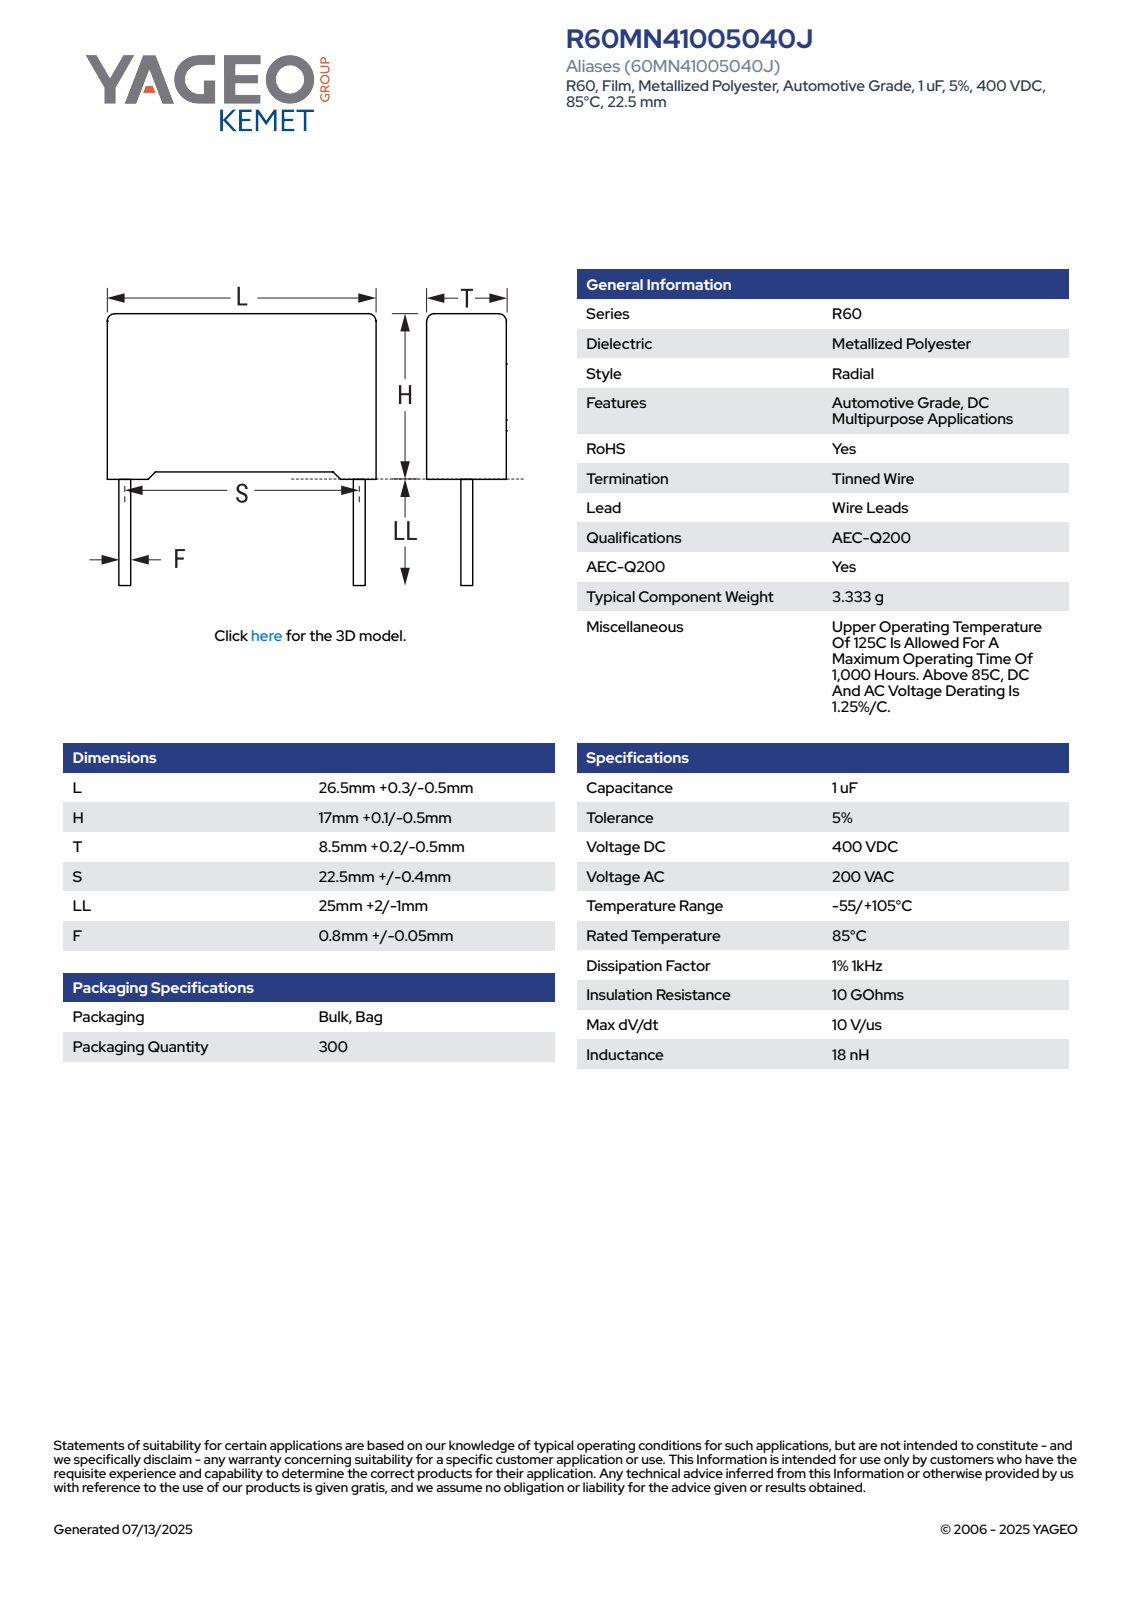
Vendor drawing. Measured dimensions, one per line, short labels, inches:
name: CFR_RB2_26.5X17X8.5_L26.8H17.1T8.7S22.5LL27F0.85
written by: SolidWorks 2021 (AUTOMOTIVE_DESIGN)
unit: in
bodies: 4 solids, 85 faces (77 planar, 8 cylindrical, 0 other)
size: 1.736 × 1.055 × 0.343
volume: 0.236 in³; area: 2.902 in²
bosses: 2× ⌀0.033
rounds: 4× R0.02
face distances: 0.343, 0.644, 1.055, 0.65, 0.035, 0.03, 0.023, 0.673, 0.307, 0.343
